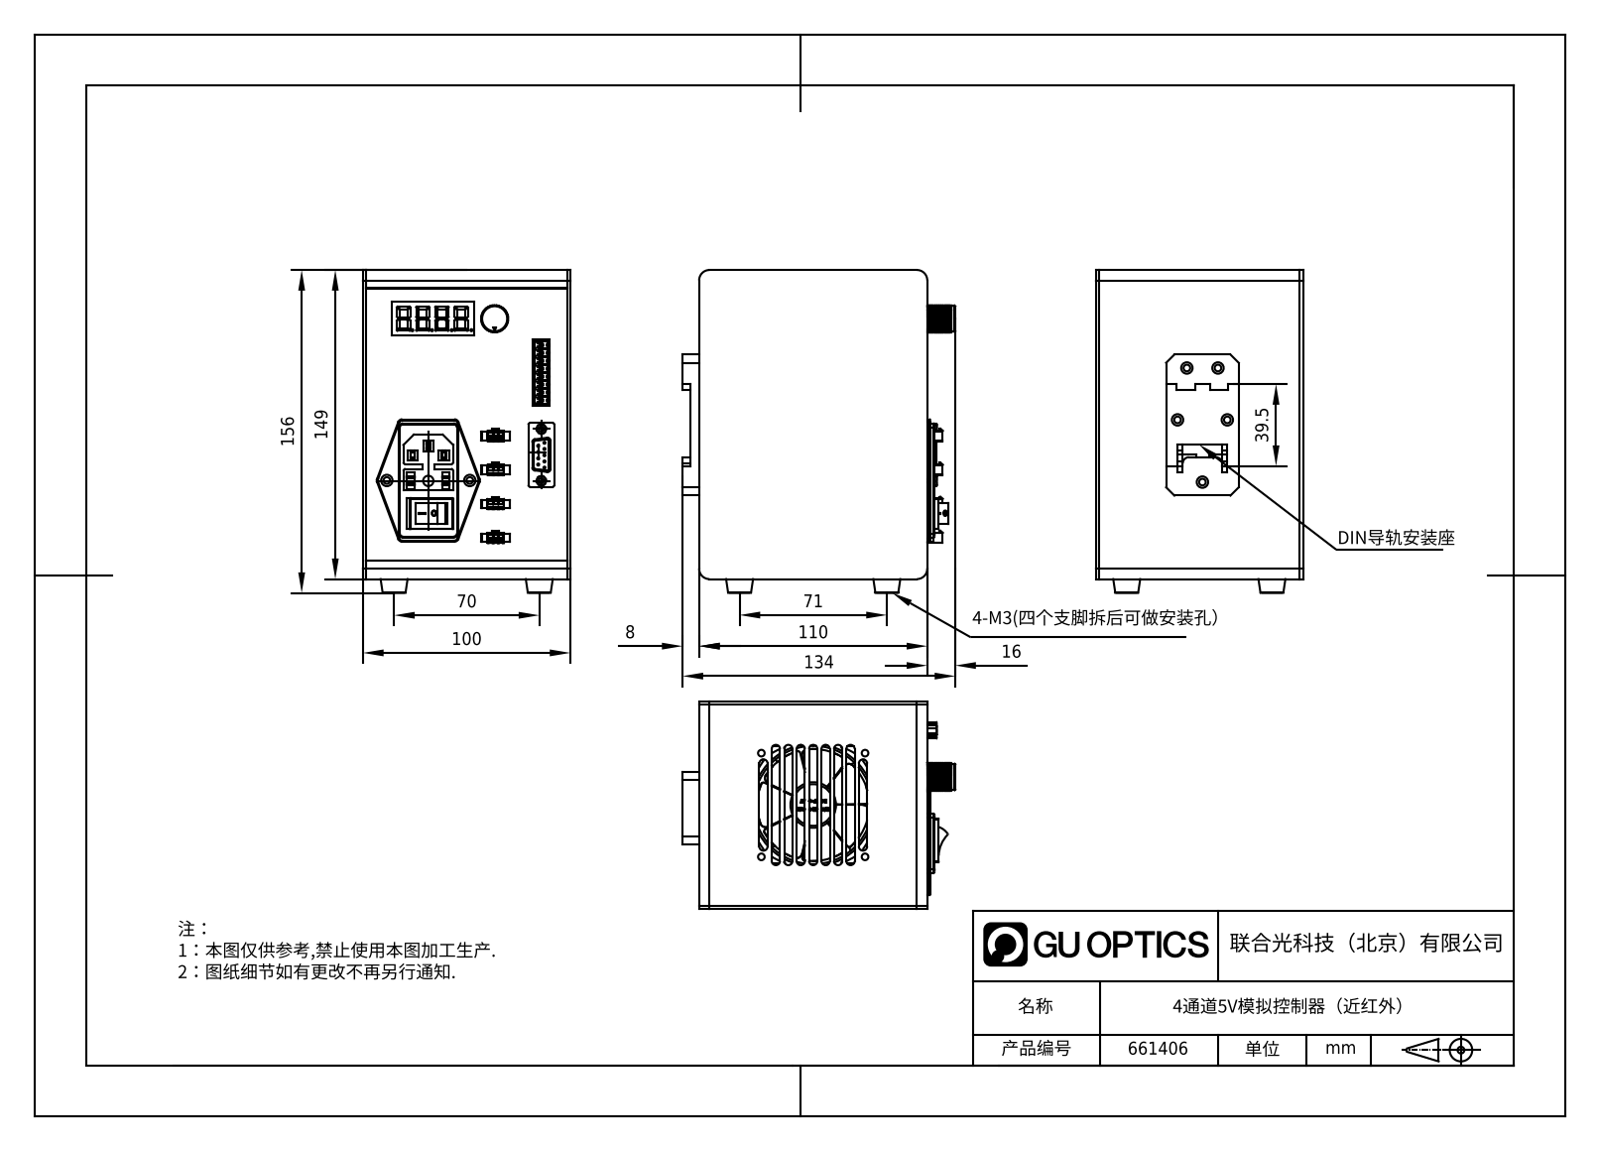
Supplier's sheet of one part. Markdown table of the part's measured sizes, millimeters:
| quantity | value |
| --- | --- |
| part name | 661406 |
| STEP written by | SolidWorks 2020 (CONFIG_CONTROL_DESIGN) |
| units | millimeters |
| bodies | 33 solids, 5052 faces (3996 planar, 621 cylindrical, 435 other) |
| overall size | 155.7 × 131.5 × 100 |
| volume | 250 832 mm³ |
| surface area | 220 794 mm² |
| round holes (diameter × count) | 3.2 × 15, 1 × 13, 3 × 6, 5.6 × 4, 4.5 × 3, 2.4 × 2, 2.5 × 2, 2.54 × 1, 2.6 × 1, 3.5 × 1, 5 × 1, 5.24 × 1 |
| round bosses / shafts (diameter × count) | 0.6 × 12, 2 × 8, 2.99 × 2, 22 × 1, 12.7 × 1, 12.68 × 1, 6 × 1, 3 × 1 |
| partial cylindrical surfaces (radius × count) | 0.2 × 123, 0.3 × 46, 0.5 × 32, 2 × 30, 0.4 × 24, 3 × 17, 1 × 16, 0.33 × 8 |
| main face-to-face distances | 1.5, 98.5, 3, 97, 100, 2, 108.5, 105.5, 106.5, 103.5 |
| hole center spacings | 3.35, 3, 5.41, 6, 8.08, 14.5, 35.36, 49.85 |
